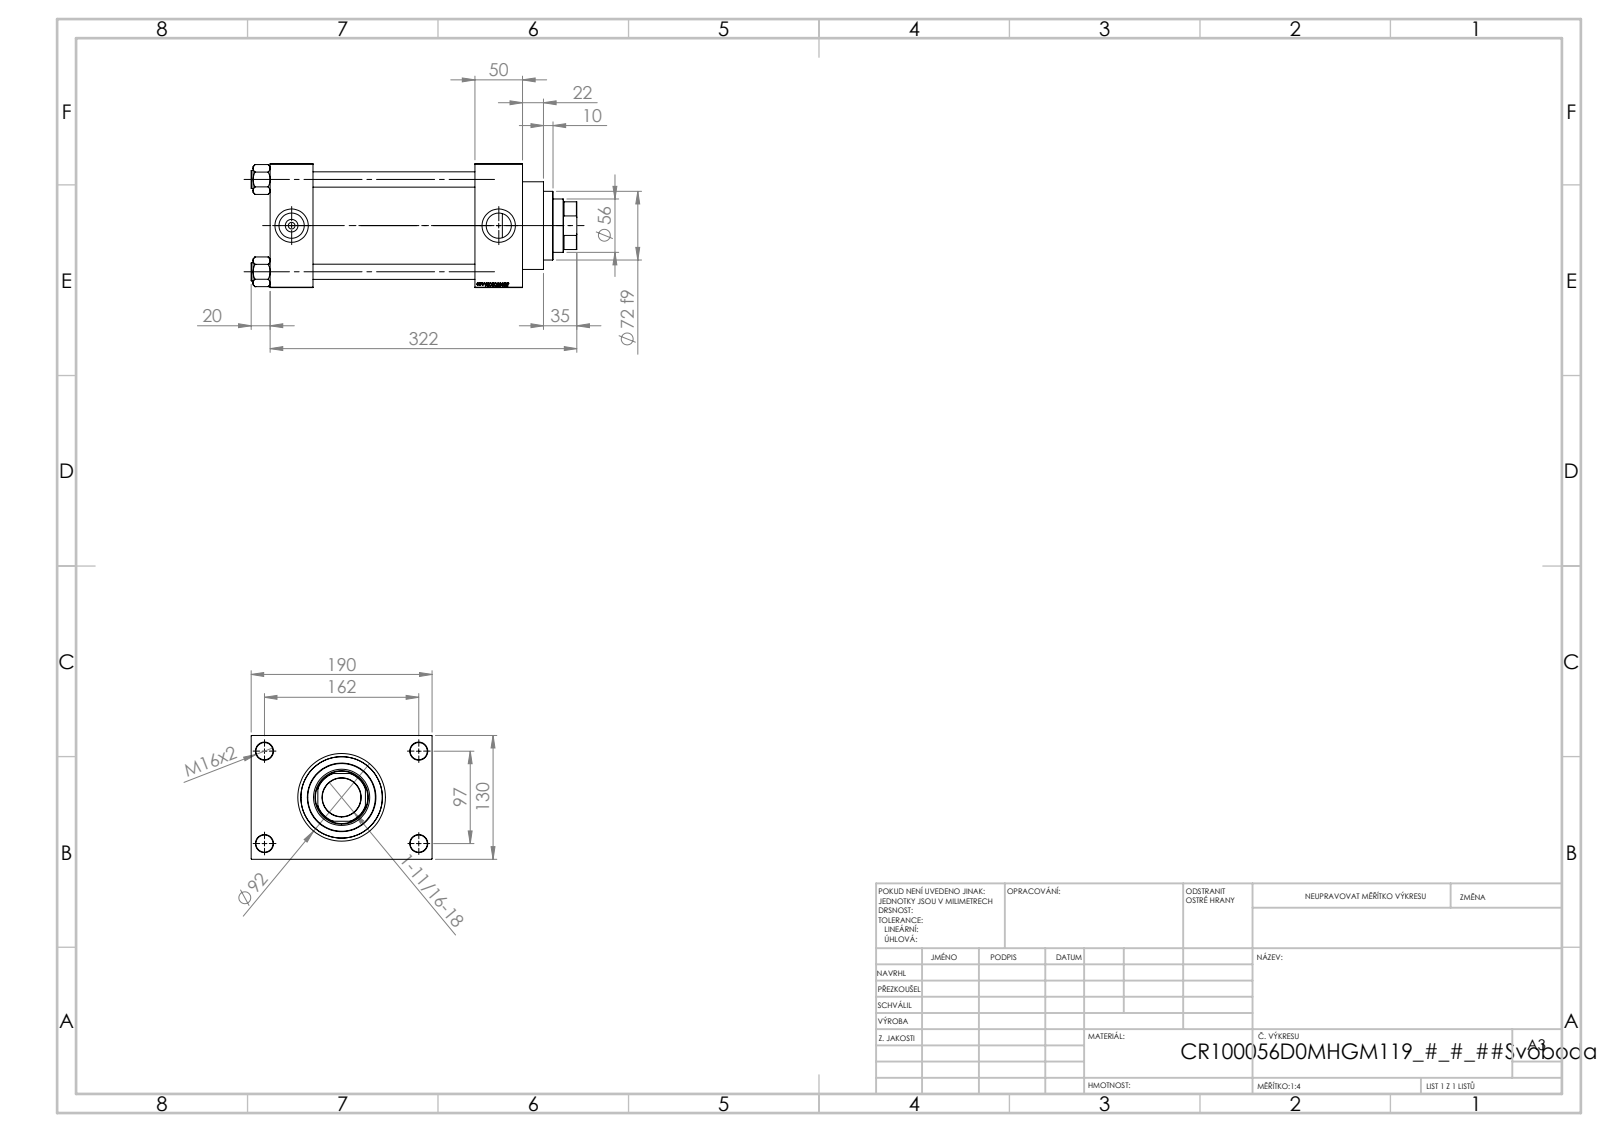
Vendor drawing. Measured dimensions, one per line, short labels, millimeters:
name: V215CR_VCP_D; V215CR_D_TYCINKA; V215CR_D_Body; V215_VC_A (+1 more)
written by: SolidWorks 2019 (CONFIG_CONTROL_DESIGN)
unit: mm
bodies: 11 solids, 1151 faces (545 planar, 88 cylindrical, 518 other)
size: 342 × 190 × 130
volume: 3 048 000 mm³; area: 463 755 mm²
holes: 4× ⌀16, 4× ⌀18, 2× ⌀7, 2× ⌀26.44, 2× ⌀35, 1× ⌀40.5, 1× ⌀56, 1× ⌀59, 1× ⌀76, 1× ⌀85.5, 1× ⌀100
bosses: 4× ⌀19, 1× ⌀106, 1× ⌀92, 1× ⌀72
rounds: 1× R27
face distances: 130, 50, 45, 215, 170, 265, 220, 30, 160, 190
hole spacings: 32.55, 68.52, 94.41, 96.9, 102.27, 129.45, 161.73, 97
